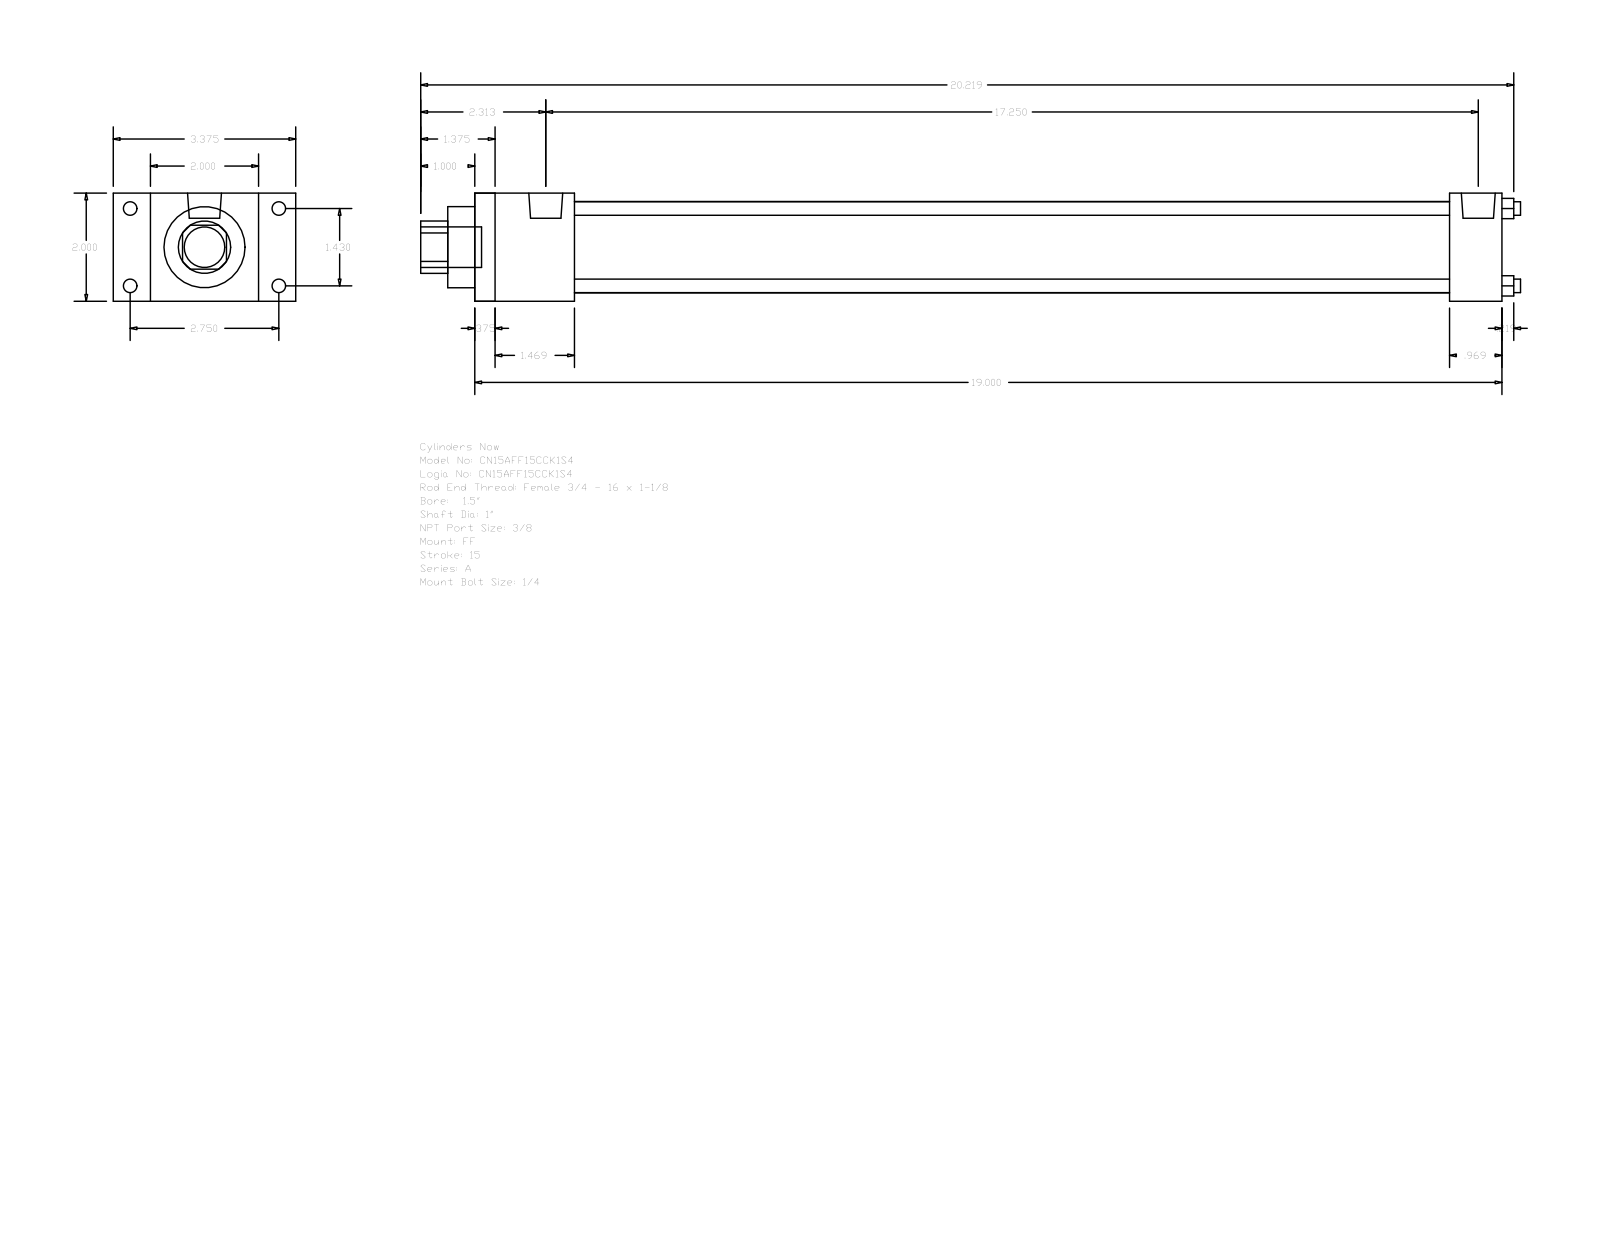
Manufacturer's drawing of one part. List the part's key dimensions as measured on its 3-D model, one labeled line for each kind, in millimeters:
Part name (STEP PRODUCT): A_FF__0150_1
STEP written by: GSSL Pune (CONFIG_CONTROL_DESIGN)
Units: millimetres
Bodies: 0 solids, 92 faces (64 planar, 28 cylindrical, 0 other)
Overall size (bounding box): 516.73 × 85.72 × 50.8
Round holes (diameter × count): ⌀6.35 ×4, ⌀25.4 ×1, ⌀38.1 ×1, ⌀42.93 ×1
Round bosses / shafts (diameter × count): ⌀6.35 ×4, ⌀5.56 ×4, ⌀15.93 ×2, ⌀19.05 ×1
Partial cylindrical surfaces — rounded edges, fillets, slot ends (radius × count): R12.29 ×1
Main face-to-face distances: 50.8, 482.6, 9.52, 473.08, 46.83, 457.99, 37.31, 448.47, 411.16, 435.77
Hole centre spacings: 25.68, 36.32, 51.36
